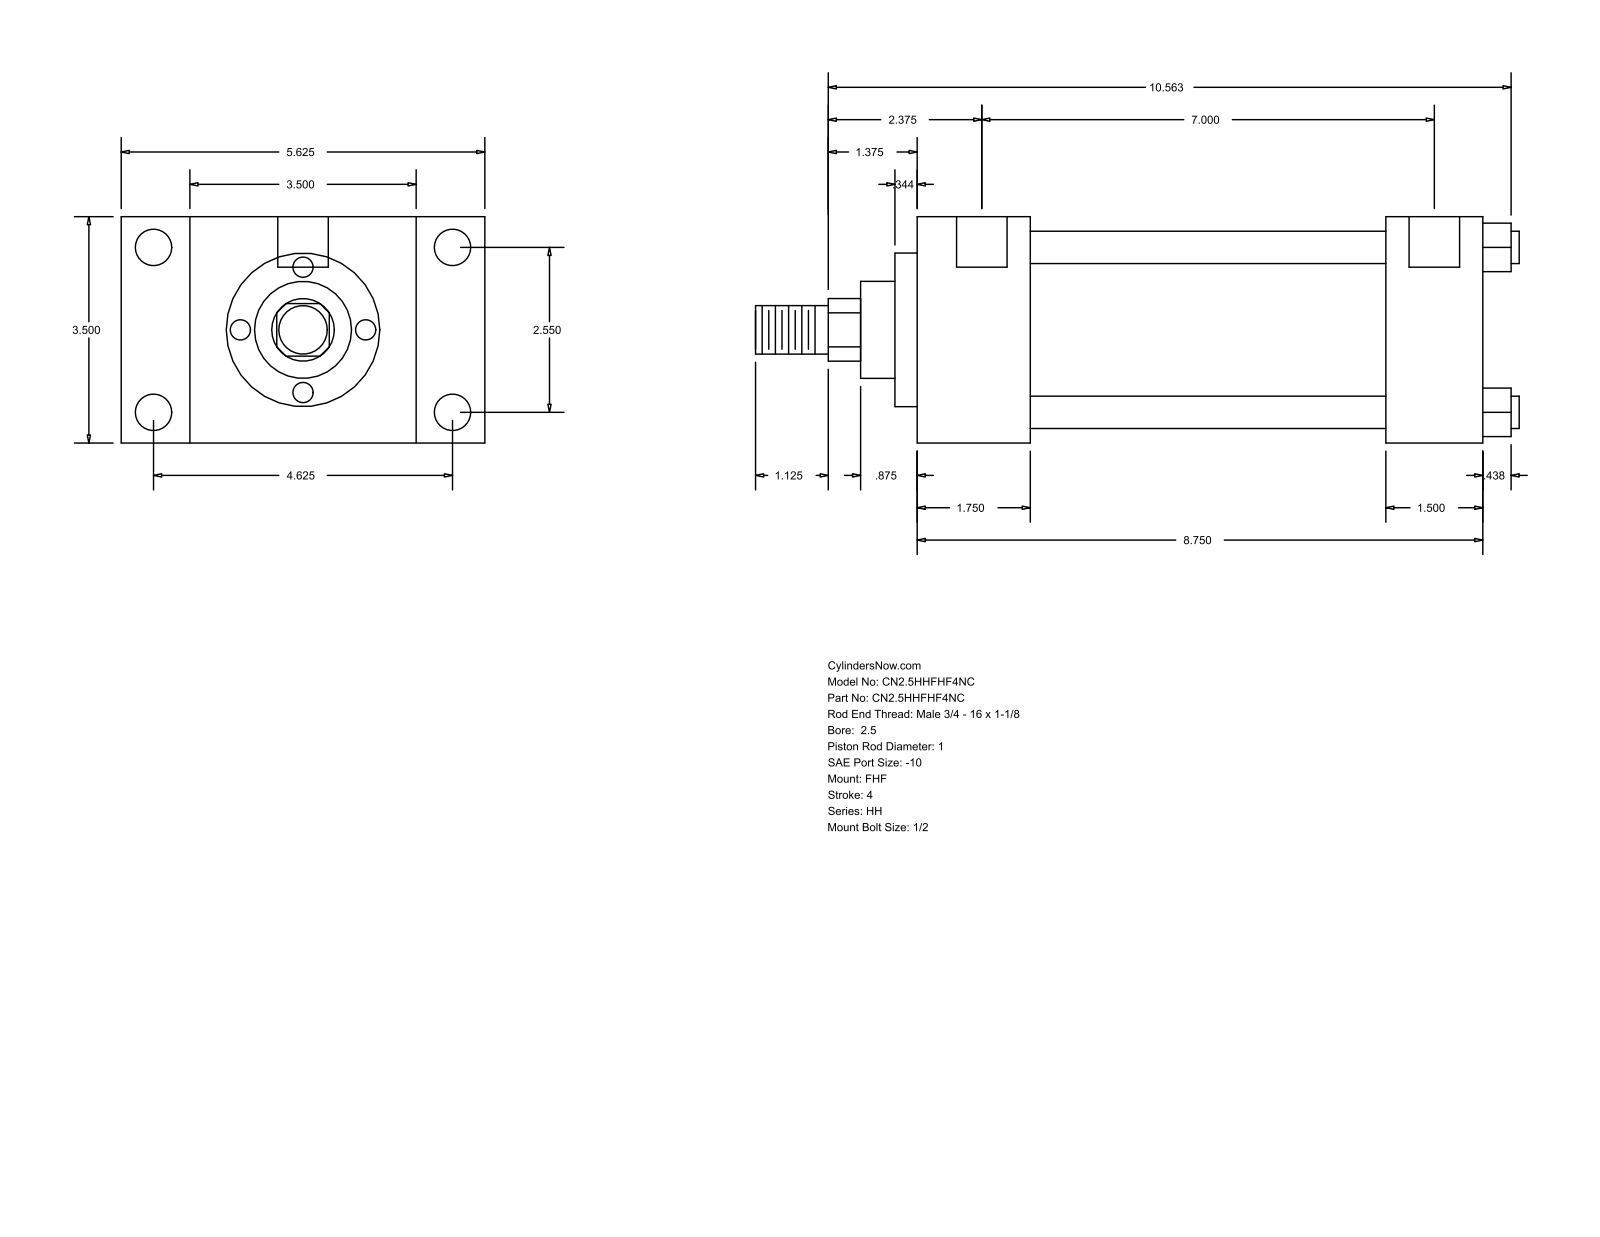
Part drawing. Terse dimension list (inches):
name: HH_FHF__0250_1
written by: GSSL Pune (CONFIG_CONTROL_DESIGN)
unit: in
bodies: 0 solids, 90 faces (61 planar, 29 cylindrical, 0 other)
size: 11.813 × 5.625 × 3.5
holes: 4× ⌀0.219, 4× ⌀0.563, 2× ⌀0.781
bosses: 4× ⌀0.5, 1× ⌀2.875, 1× ⌀2.375, 1× ⌀1.5, 1× ⌀1, 1× ⌀0.75
rounds: 1× R0.484
face distances: 3.5, 1.75, 1.063, 4.563, 8.75, 7, 5.625, 7.25, 5.5, 1.5
hole spacings: 0.063, 2.55, 4.625, 5.281, 7.062, 7.125, 7
